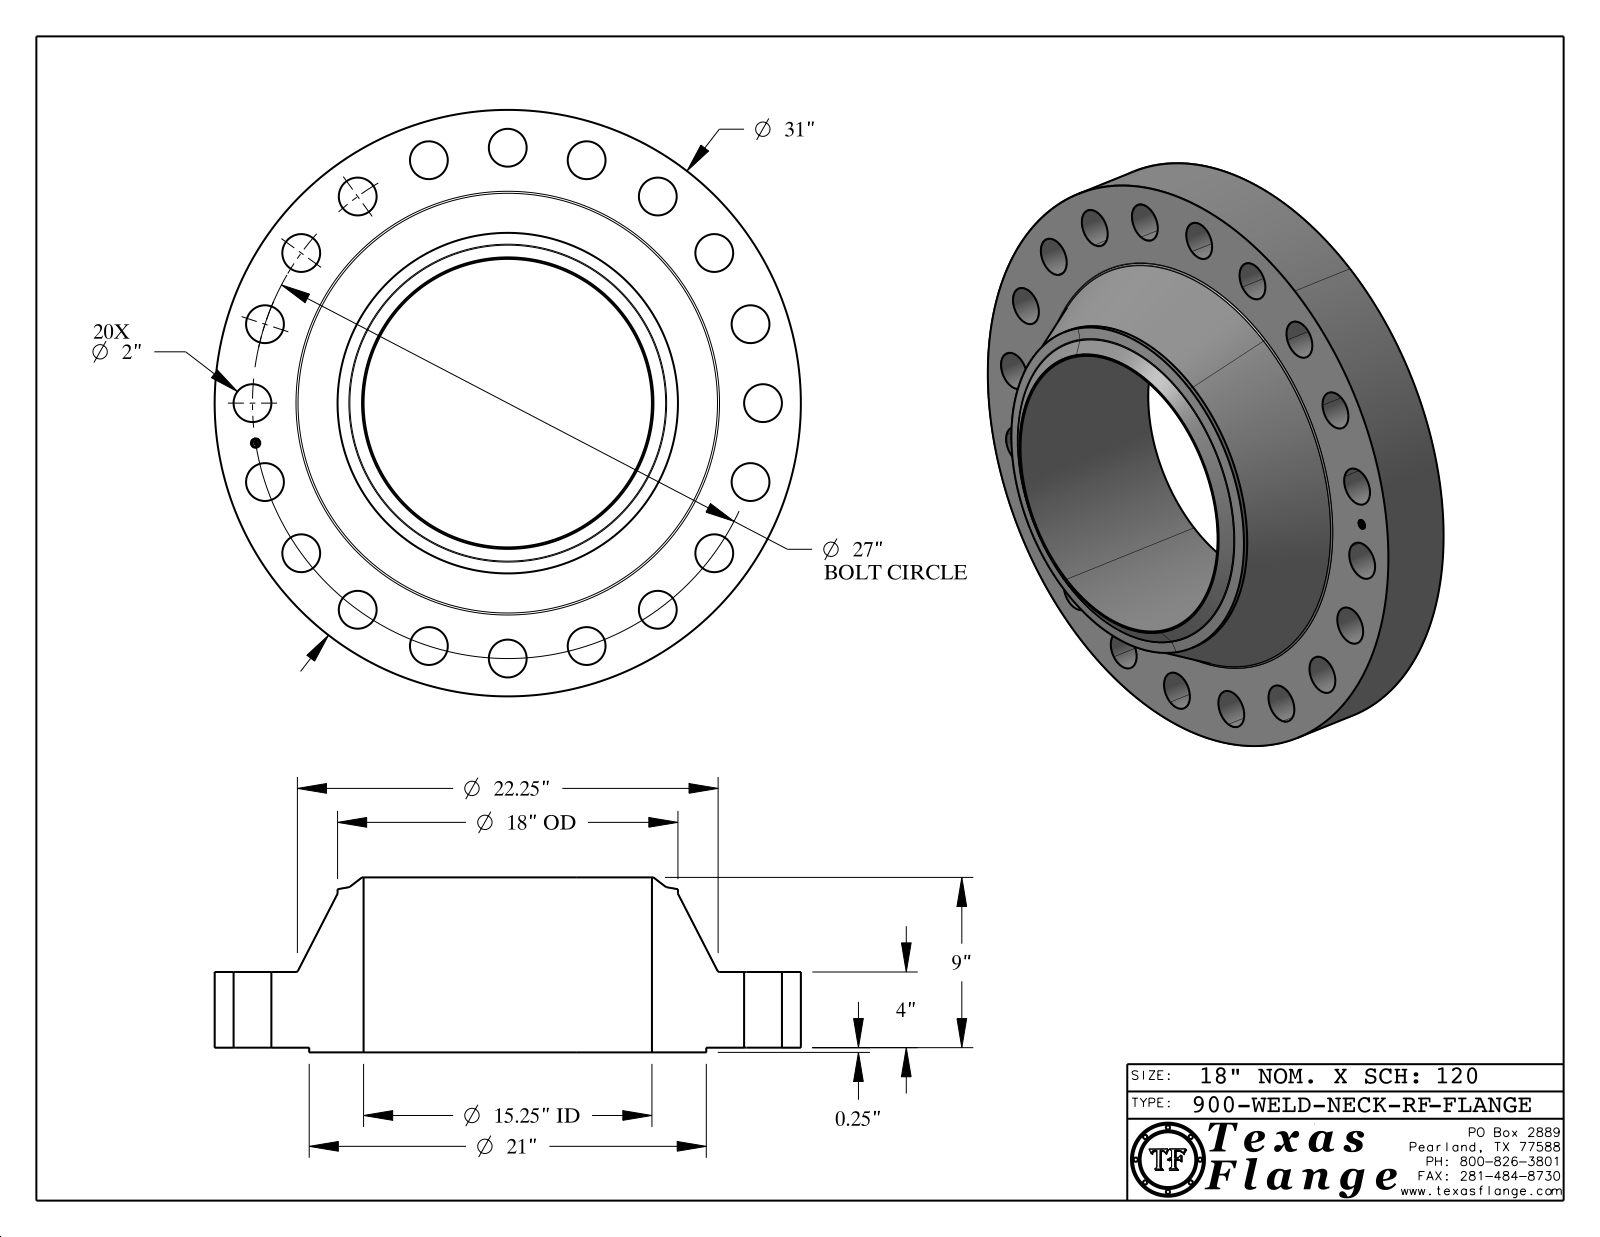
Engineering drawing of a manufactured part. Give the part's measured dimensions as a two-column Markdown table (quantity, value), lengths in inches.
| quantity | value |
| --- | --- |
| part name | 900-WELD-NECK-RF |
| STEP written by | CATIA V5 STEP AP214 (AUTOMOTIVE_DESIGN) |
| units | inches |
| bodies | 1 solid, 447 faces (369 planar, 68 cylindrical, 10 other) |
| overall size | 31 × 31 × 9.25 |
| volume | 2 677 in³ |
| surface area | 2 552 in² |
| round holes (diameter × count) | 2 × 20, 0.495 × 1, 15.25 × 1 |
| round bosses / shafts (diameter × count) | 0.03 × 8, 31 × 1, 21 × 1, 18 × 1, 0.39 × 1 |
| main face-to-face distances | 4, 0.25, 4.25, 9.25, 9, 5, 4.235, 3.985, 0.015, 5.015 |
| hole center spacings | 13.5, 21.843, 24.057, 25.678, 26.668, 4.224, 8.343, 12.258 |
